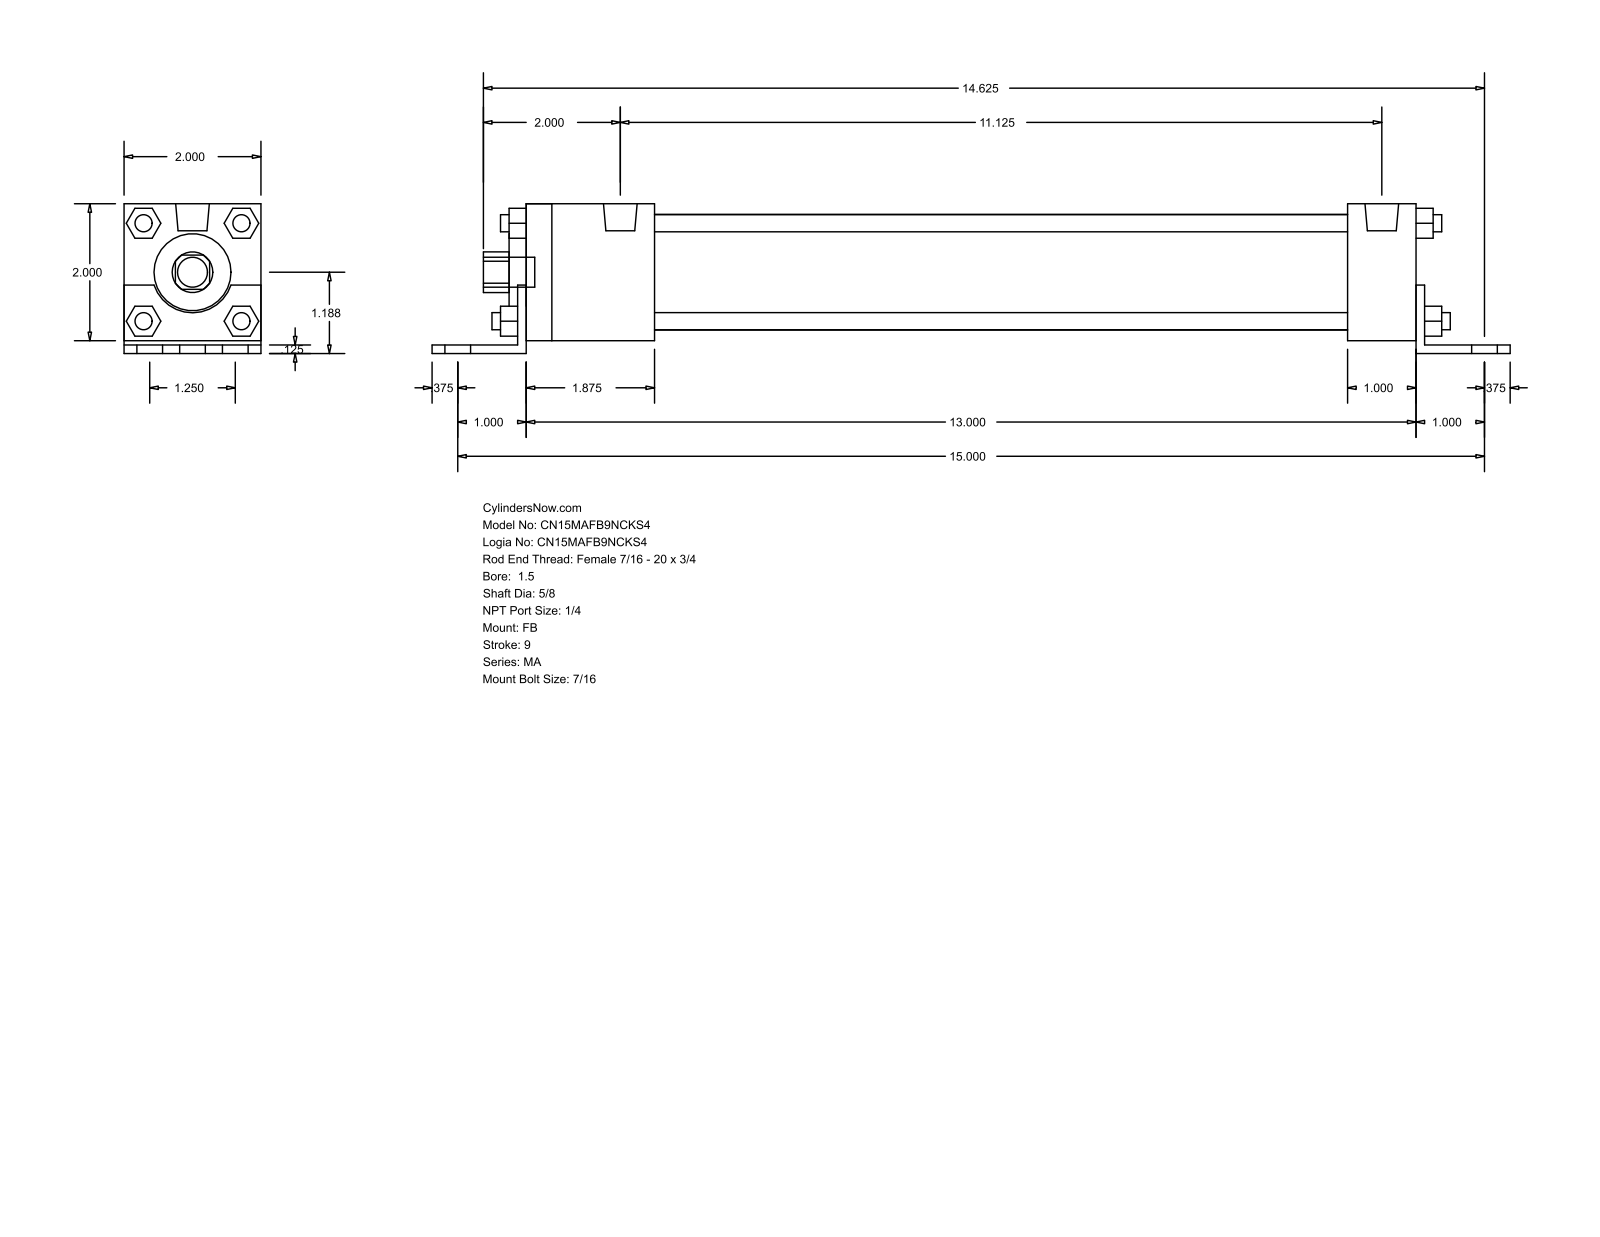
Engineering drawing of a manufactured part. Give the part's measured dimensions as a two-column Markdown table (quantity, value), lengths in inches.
| quantity | value |
| --- | --- |
| part name | MA_FB__0150_0.625 |
| STEP written by | GSSL Pune (CONFIG_CONTROL_DESIGN) |
| units | inches |
| bodies | 0 solids, 140 faces (105 planar, 35 cylindrical, 0 other) |
| overall size | 15.75 × 2.187 × 2 |
| round holes (diameter × count) | 0.625 × 1, 1.125 × 1, 1.69 × 1 |
| round bosses / shafts (diameter × count) | 0.437 × 7, 0.313 × 4, 0.25 × 4, 0.492 × 2 |
| partial cylindrical surfaces (radius × count) | 0.297 × 1, 0.593 × 1 |
| main face-to-face distances | 2, 0.125, 0.187, 2.187, 0.063, 2.063, 0.125, 13.125, 0.25, 13 |
